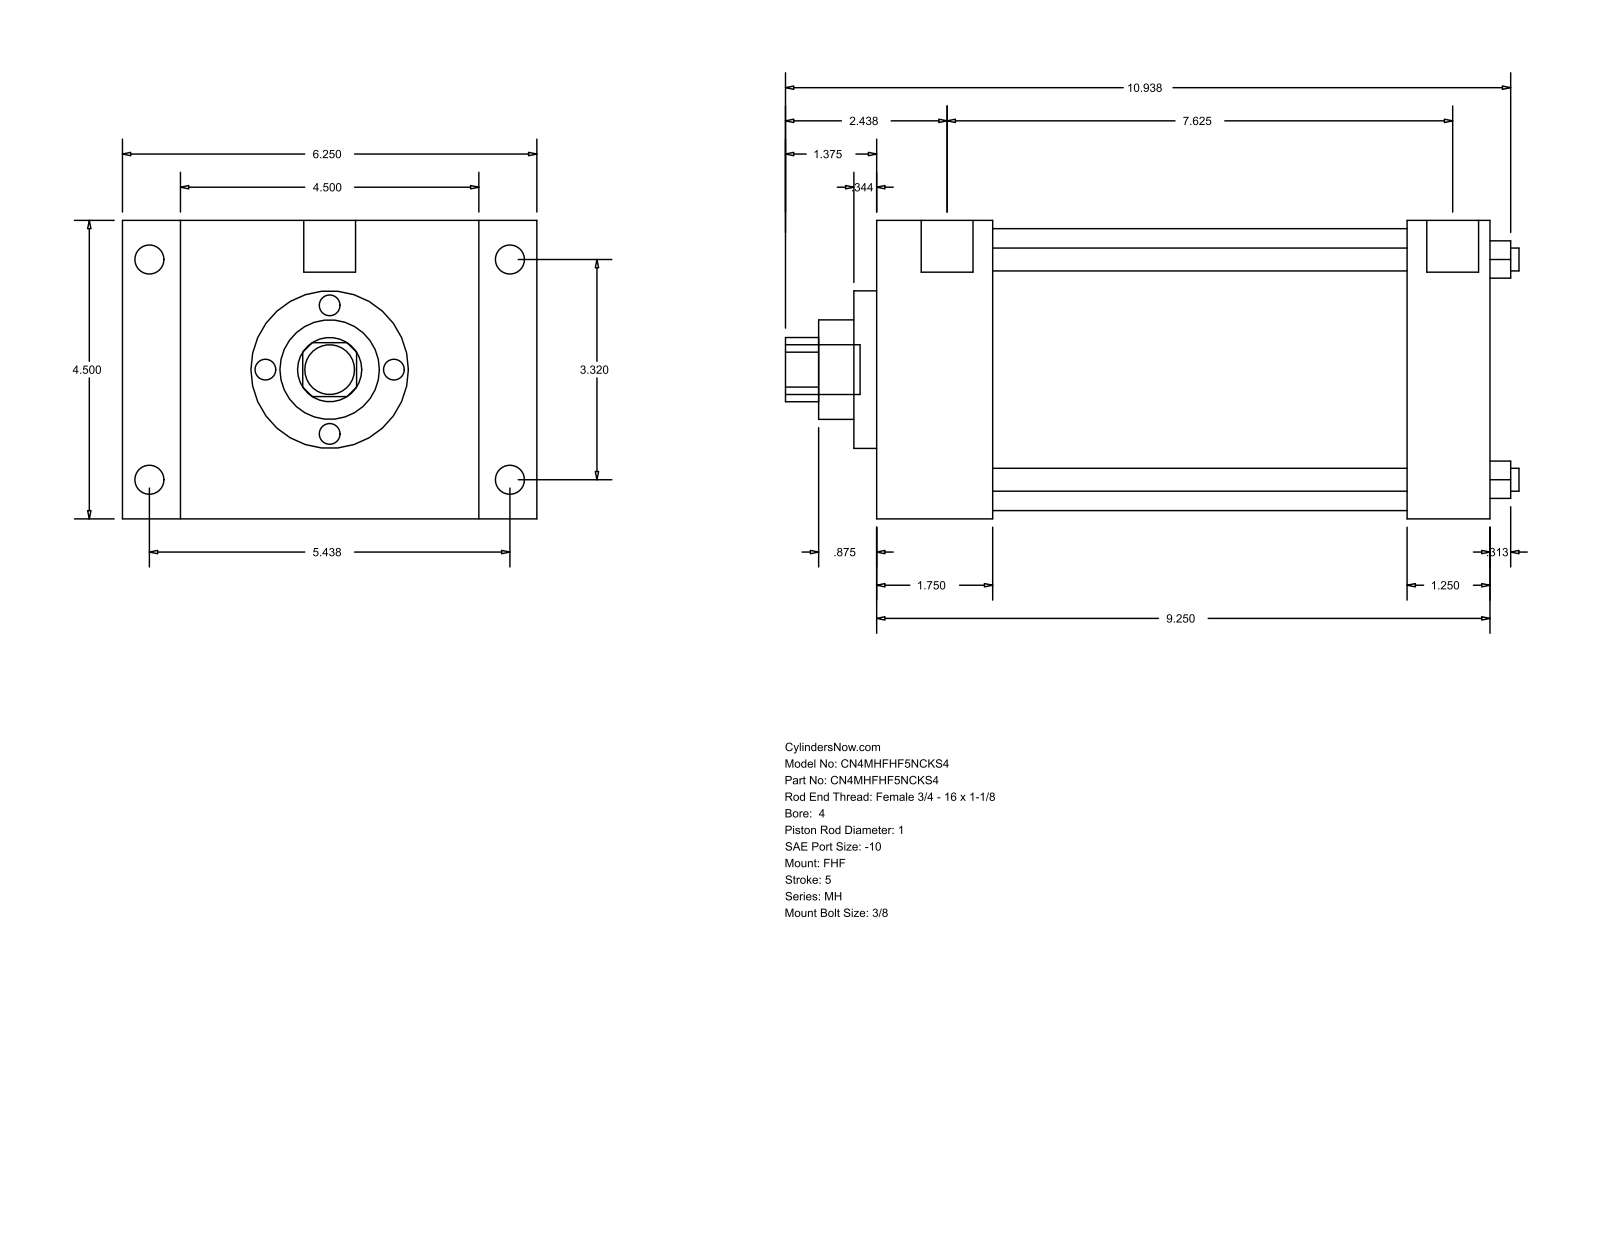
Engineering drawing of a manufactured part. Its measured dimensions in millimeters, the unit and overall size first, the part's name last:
Units: millimetres
Overall size (bounding box): 280.99 × 158.75 × 114.3
Round holes (diameter × count): ⌀8.76 ×4, ⌀25.4 ×1, ⌀38.1 ×1, ⌀60.33 ×1, ⌀107.95 ×1
Round bosses / shafts (diameter × count): ⌀11.13 ×4, ⌀8.73 ×4, ⌀19.84 ×2, ⌀19.05 ×1
Partial cylindrical surfaces — rounded edges, fillets, slot ends (radius × count): R12.29 ×1
Main face-to-face distances: 114.3, 234.96, 44.46, 190.5, 22.23, 136.53, 158.76, 158.74, 203.2, 31.76
Hole centre spacings: 59.62, 84.32, 119.25
Bodies: 0 solids, 90 faces (61 planar, 29 cylindrical, 0 other)
Part name (STEP PRODUCT): MH_FHF__0400_1
STEP written by: GSSL Pune (CONFIG_CONTROL_DESIGN)
